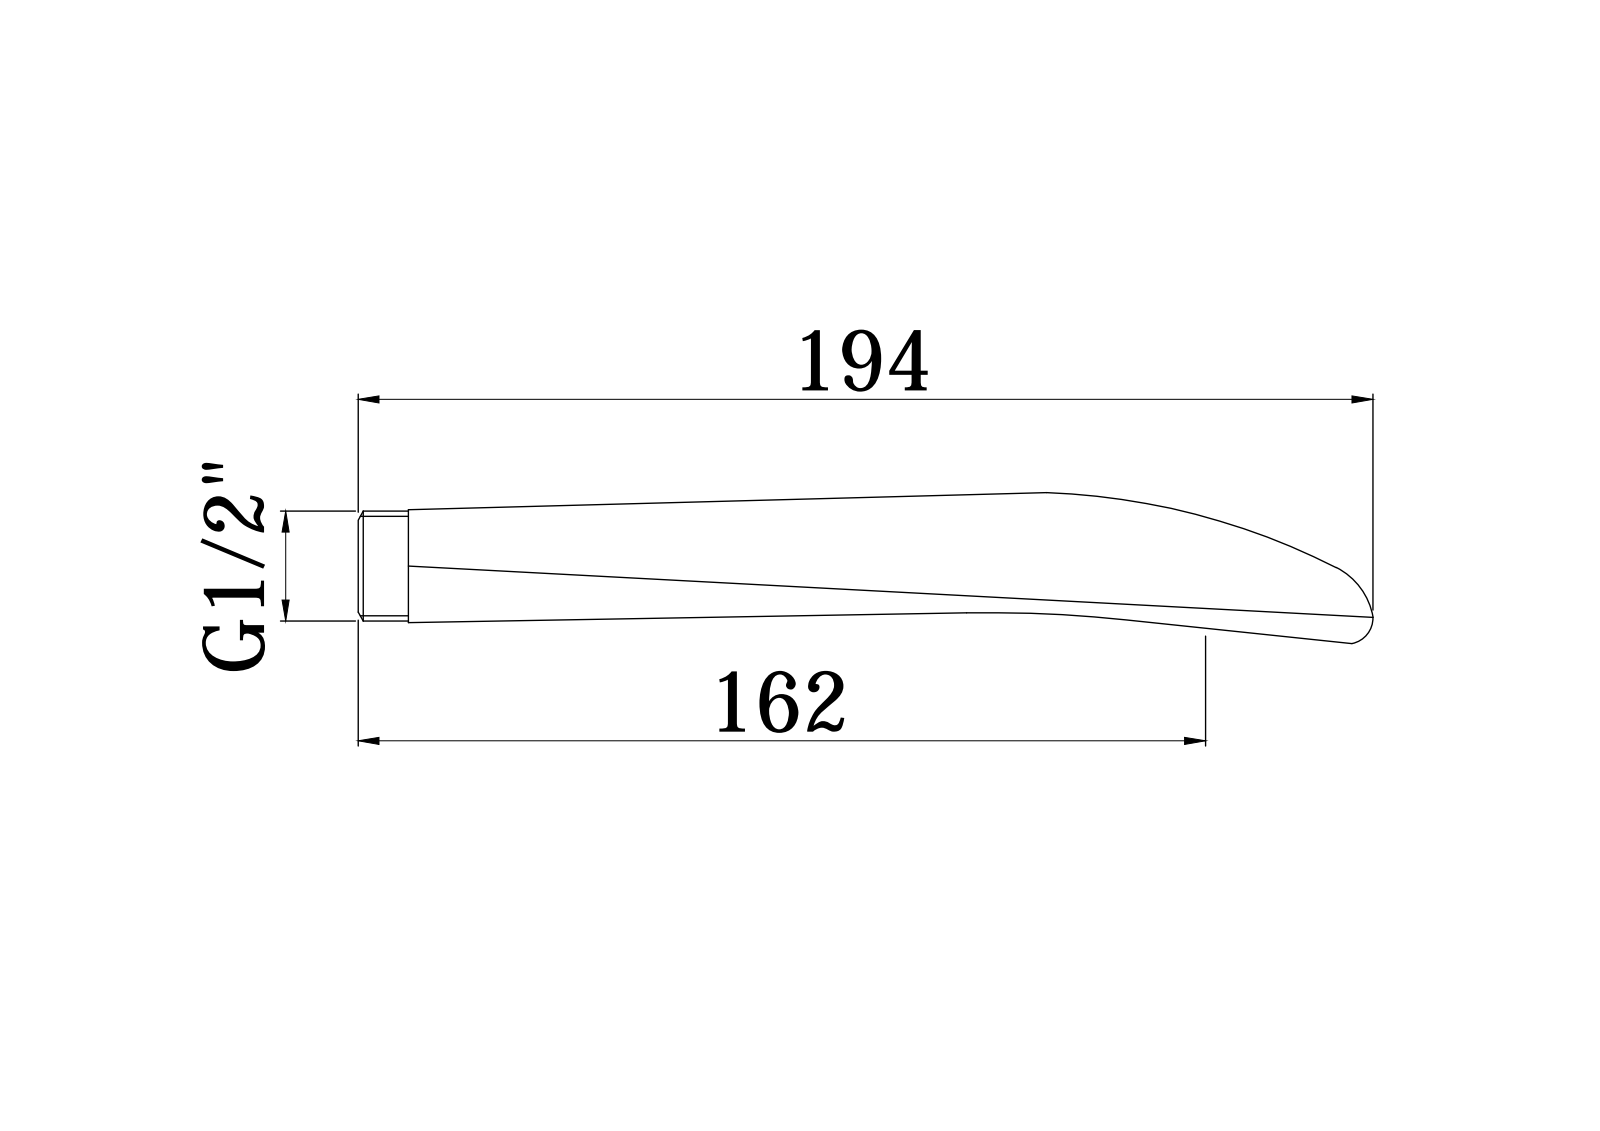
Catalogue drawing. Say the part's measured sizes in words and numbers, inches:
The part is named "ZDOC012CR". Its 3-D file was written by "CREO PARAMETRIC BY PTC INC, 2020044 (CONFIG_CONTROL_DESIGN)". It is 0 solids with 48 faces: 6 planar, 8 cylindrical and 34 other. Overall it measures 7.666 by 1.911 by 1.417 inches. Round holes: 1 of diameter 0.472, 1 of diameter 0.591. Round bosses or shafts: 1 of diameter 0.807, 1 of diameter 0.728. The main face-to-face distances are 0.02, 0.886, 0.098, 0.984, 0.118, 0.02, 0.866.
